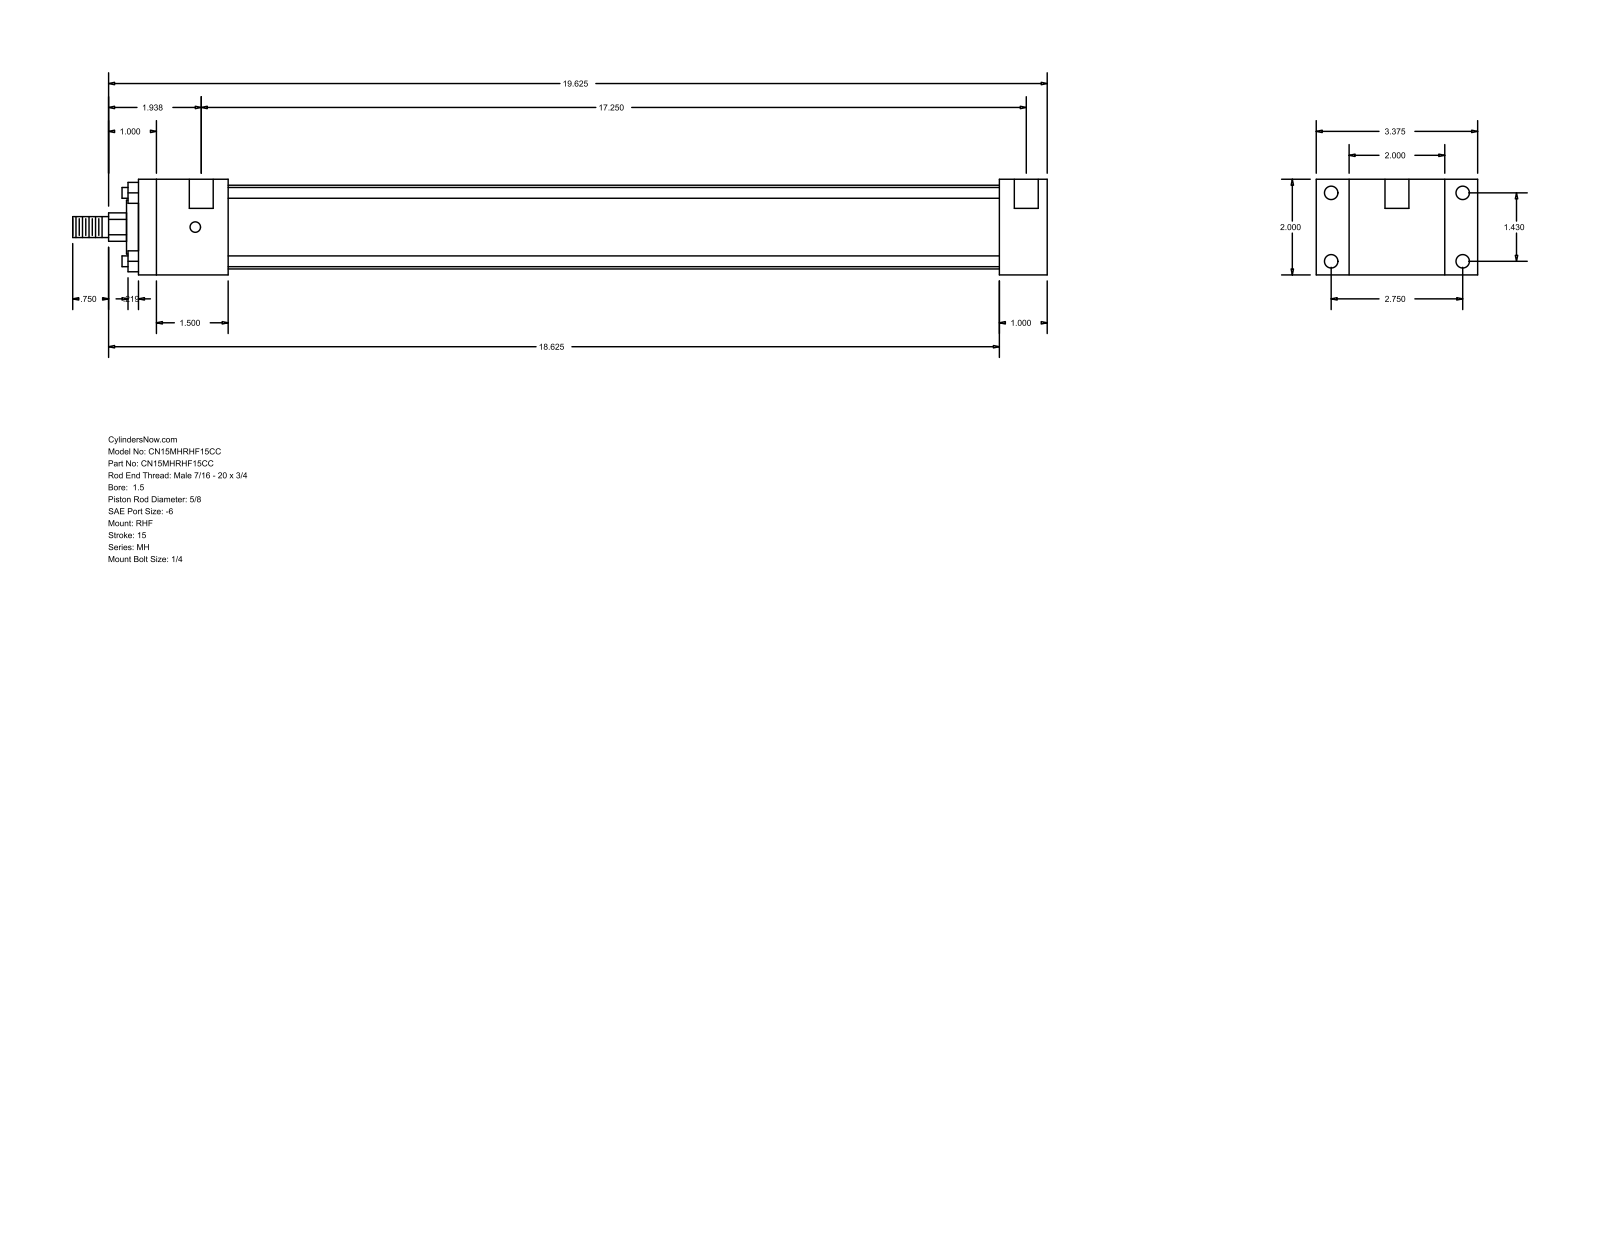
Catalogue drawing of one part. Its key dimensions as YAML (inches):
part_name: "MH_RHF__0150_0.625"
step_written_by: "GSSL Pune (CONFIG_CONTROL_DESIGN)"
units: inches
bodies: {solids: 0, faces: 88, planar: 60, cylindrical: 28, other: 0}
overall_size: [20.375, 3.375, 2]
round_holes:
  - {diameter: 0.219, count: 4}
  - {diameter: 0.281, count: 4}
  - {diameter: 0.5, count: 2}
round_bosses_or_shafts:
  - {diameter: 0.225, count: 4}
  - {diameter: 1.75, count: 1}
  - {diameter: 1.125, count: 1}
  - {diameter: 0.625, count: 1}
  - {diameter: 0.437, count: 1}
partial_cylinders:
  - {radius: 0.297, count: 1}
face_to_face_distances: [2, 0.687, 2.687, 1, 18, 19, 3.375, 1.875, 16.125, 17.125]
hole_center_spacings: [1.43, 2.75, 3.099, 17.375, 0.125, 17.25]
